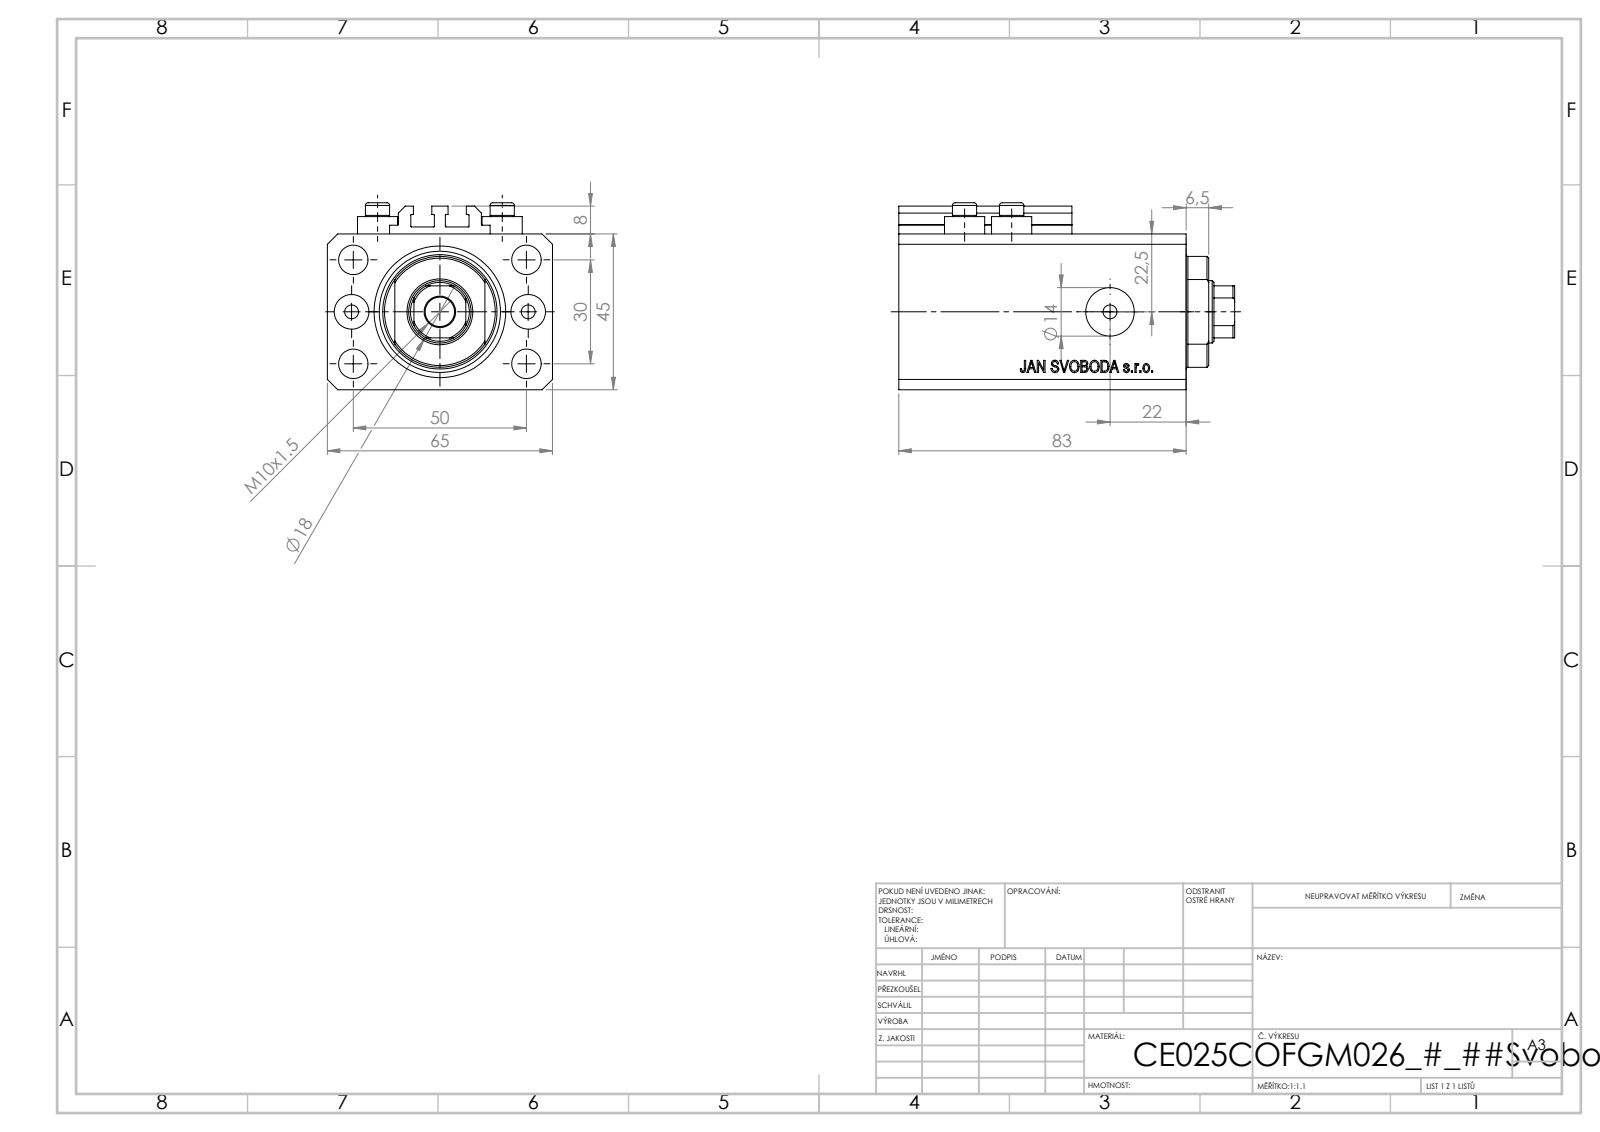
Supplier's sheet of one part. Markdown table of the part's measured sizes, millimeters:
| quantity | value |
| --- | --- |
| part name | V250CE_C_Body; V250CE_VC_C; ALLEN BOLT V250CE; V250CE_C_VCP |
| STEP written by | SolidWorks 2019 (CONFIG_CONTROL_DESIGN) |
| units | millimeters |
| bodies | 8 solids, 1034 faces (504 planar, 86 cylindrical, 444 other) |
| overall size | 97 × 65 × 54 |
| volume | 227 358 mm³ |
| surface area | 60 600 mm² |
| round holes (diameter × count) | 4 × 8, 8.5 × 5, 10 × 2, 14 × 2, 18 × 1, 25 × 1, 38 × 1 |
| round bosses / shafts (diameter × count) | 11.6 × 4, 7 × 4 |
| partial cylindrical surfaces (radius × count) | 0.2 × 10, 8.5 × 1, 16 × 1 |
| main face-to-face distances | 45, 65, 14, 69, 83, 47, 6.9, 62.1, 76.1, 3 |
| hole center spacings | 15.01, 29.15, 52.68, 13.6, 25.5, 30, 36, 38.48 |
